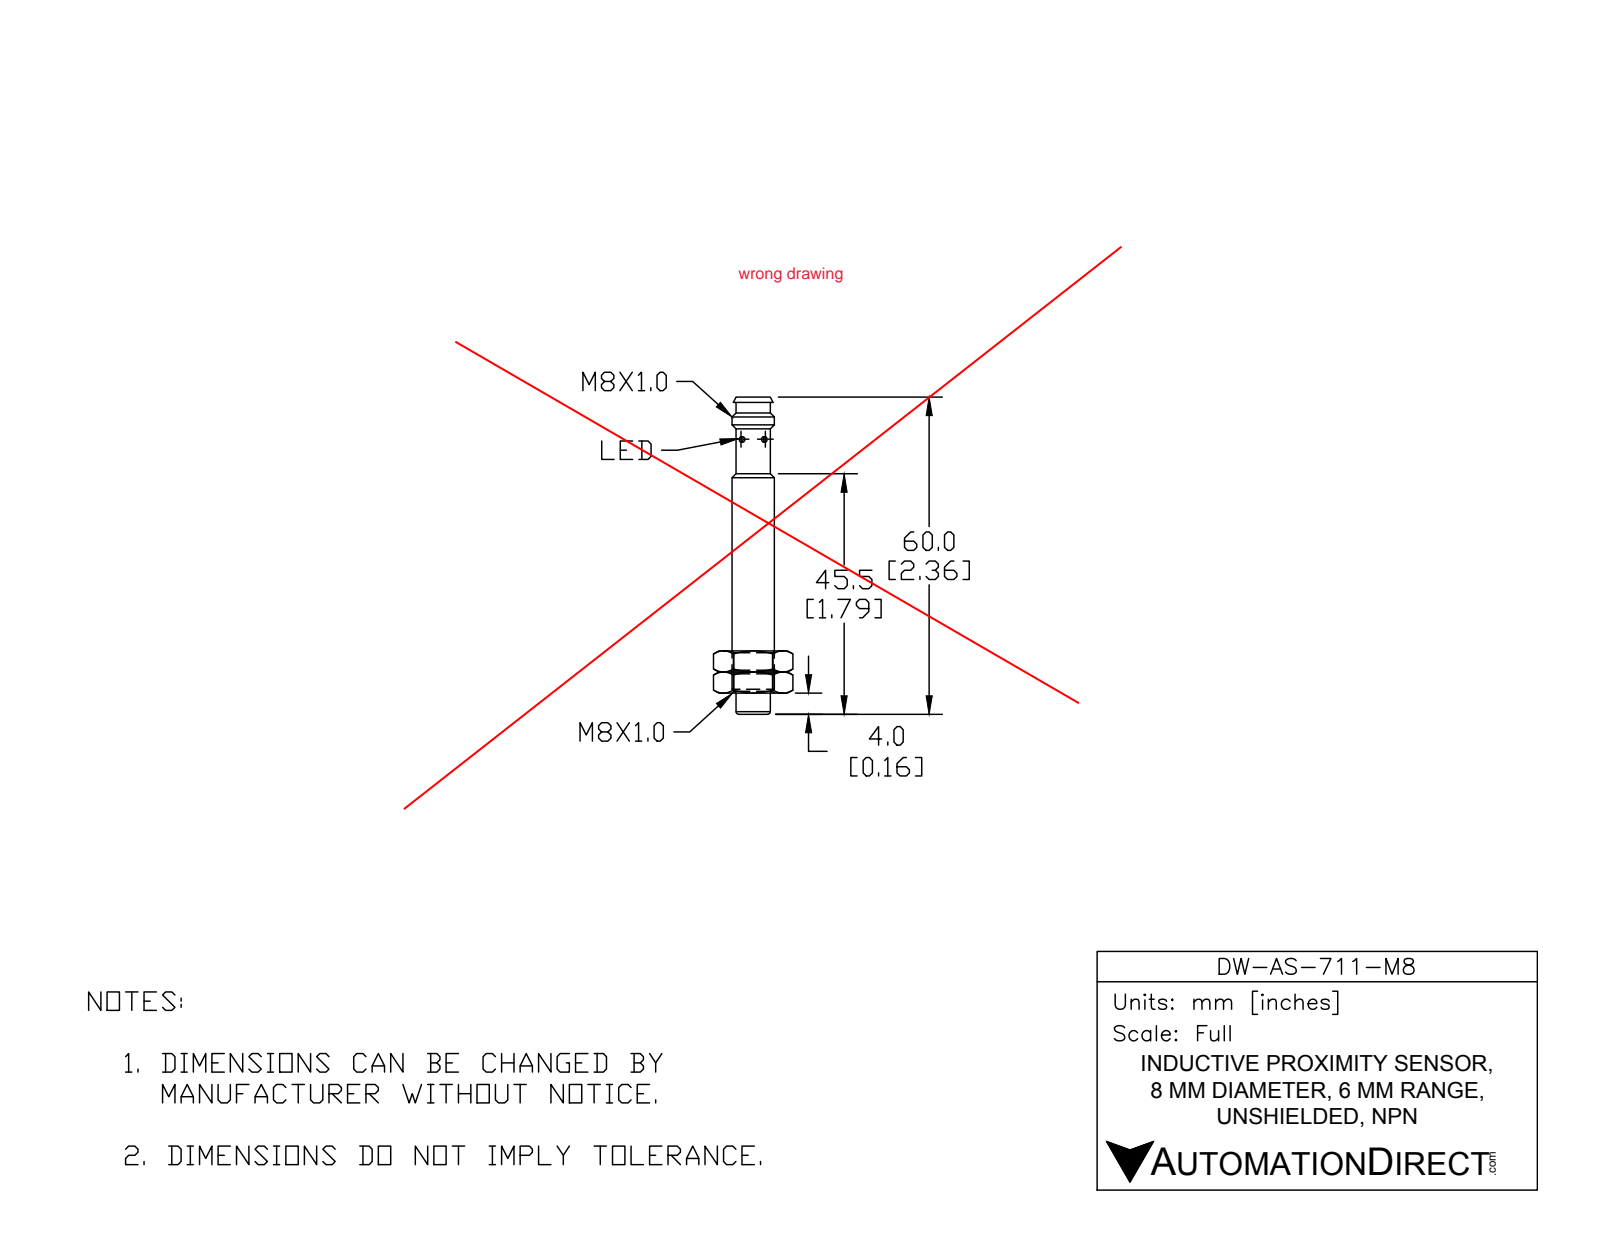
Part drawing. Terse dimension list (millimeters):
name: DW-AS-711-M8
written by: SolidWorks 2017 (AUTOMOTIVE_DESIGN)
unit: mm
bodies: 1 solid, 43 faces (7 planar, 26 cylindrical, 10 other)
size: 66 × 12 × 12
volume: 3 570 mm³; area: 2 513 mm²
holes: 2× ⌀3, 1× ⌀8.5
bosses: 4× ⌀1, 1× ⌀12, 1× ⌀10.5, 1× ⌀8, 1× ⌀6.5
rounds: 2× R0.5, 1× R0.6, 1× R4.6, 1× R4.9
face distances: 8.7, 57.3, 66, 46, 11.3, 20, 1.1, 64.5, 18.5, 7.2
